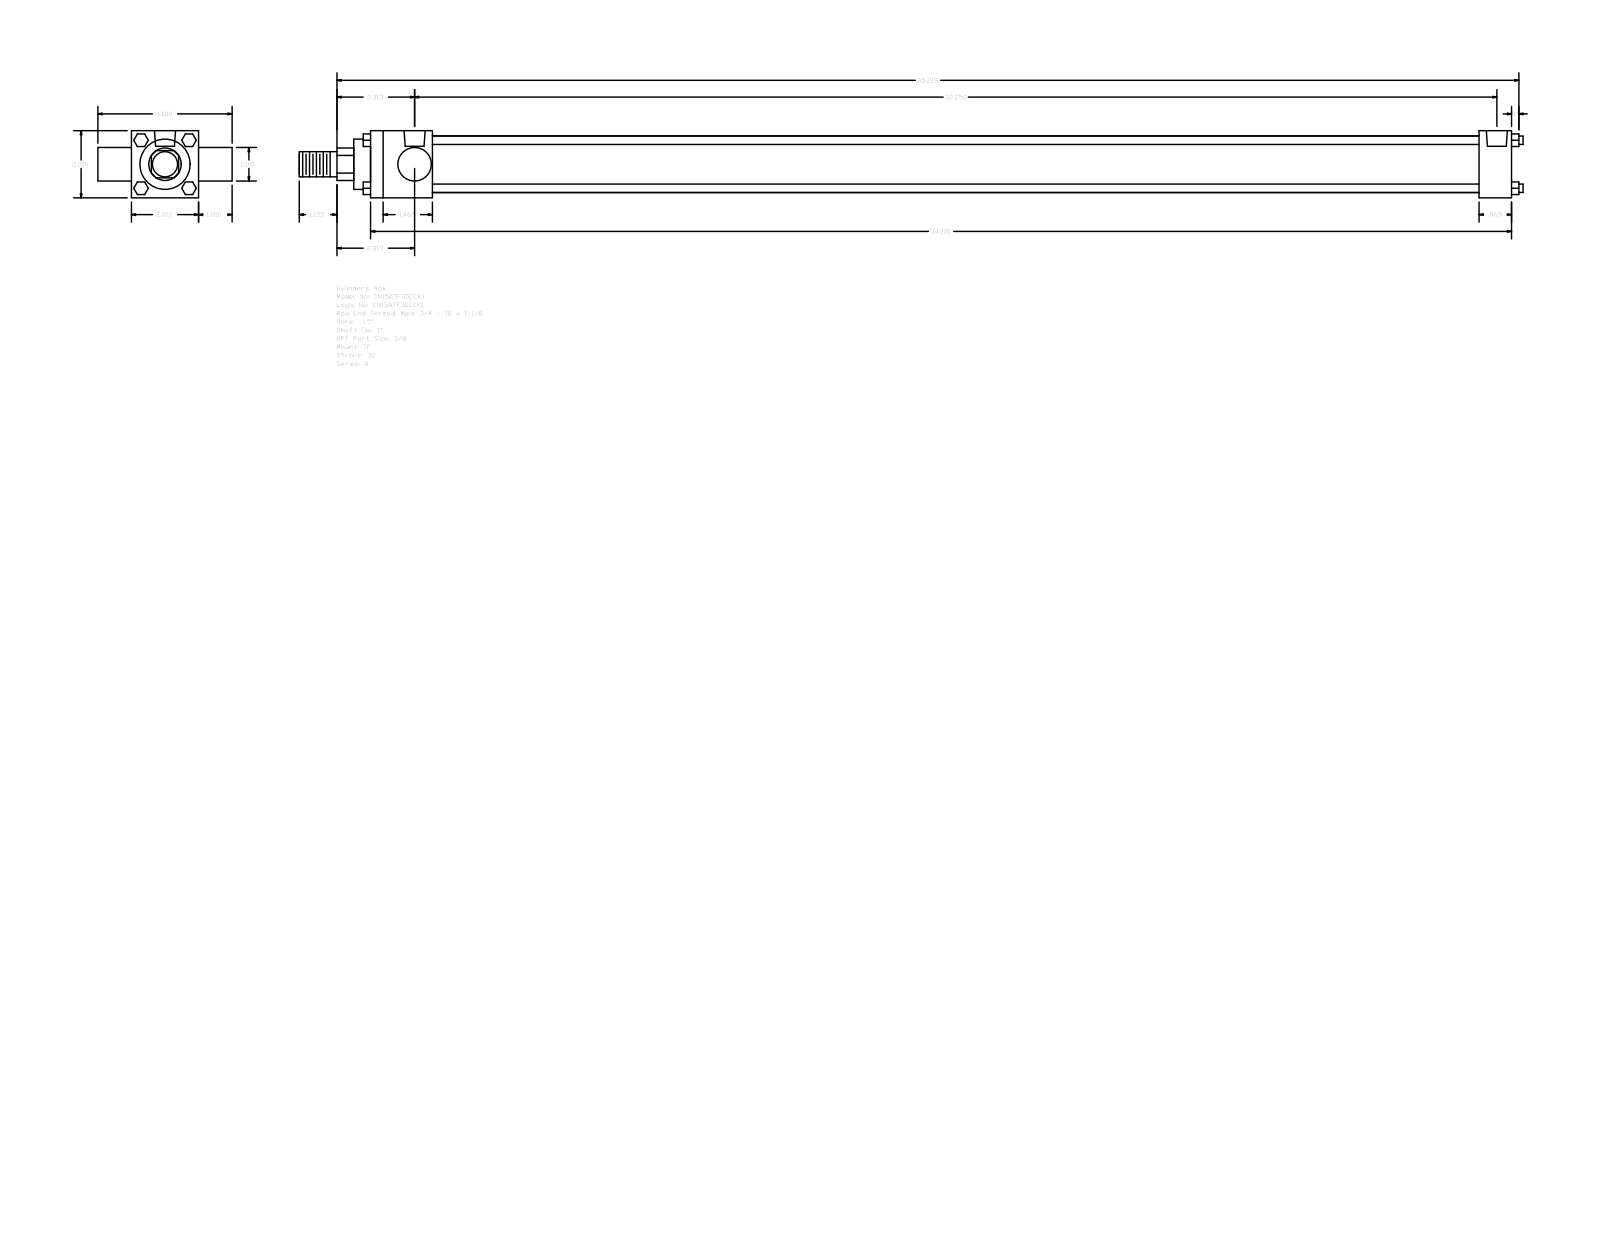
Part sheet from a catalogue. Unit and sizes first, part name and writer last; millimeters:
Units: millimetres
Overall size (bounding box): 926.31 × 101.6 × 50.8
Round holes (diameter × count): ⌀5.56 ×3, ⌀15.93 ×2
Round bosses / shafts (diameter × count): ⌀6.35 ×4, ⌀25.4 ×2, ⌀42.93 ×1, ⌀38.1 ×1, ⌀19.05 ×1
Partial cylindrical surfaces — rounded edges, fillets, slot ends (radius × count): R12.29 ×1
Main face-to-face distances: 50.8, 25.4, 863.6, 76.2, 46.83, 838.99, 792.16, 816.77, 24.61, 12.7
Hole centre spacings: 3.97, 815.18, 811.21, 819.15
Bodies: 0 solids, 120 faces (92 planar, 28 cylindrical, 0 other)
Part name (STEP PRODUCT): A_TF__0150_1
STEP written by: GSSL Pune (CONFIG_CONTROL_DESIGN)
